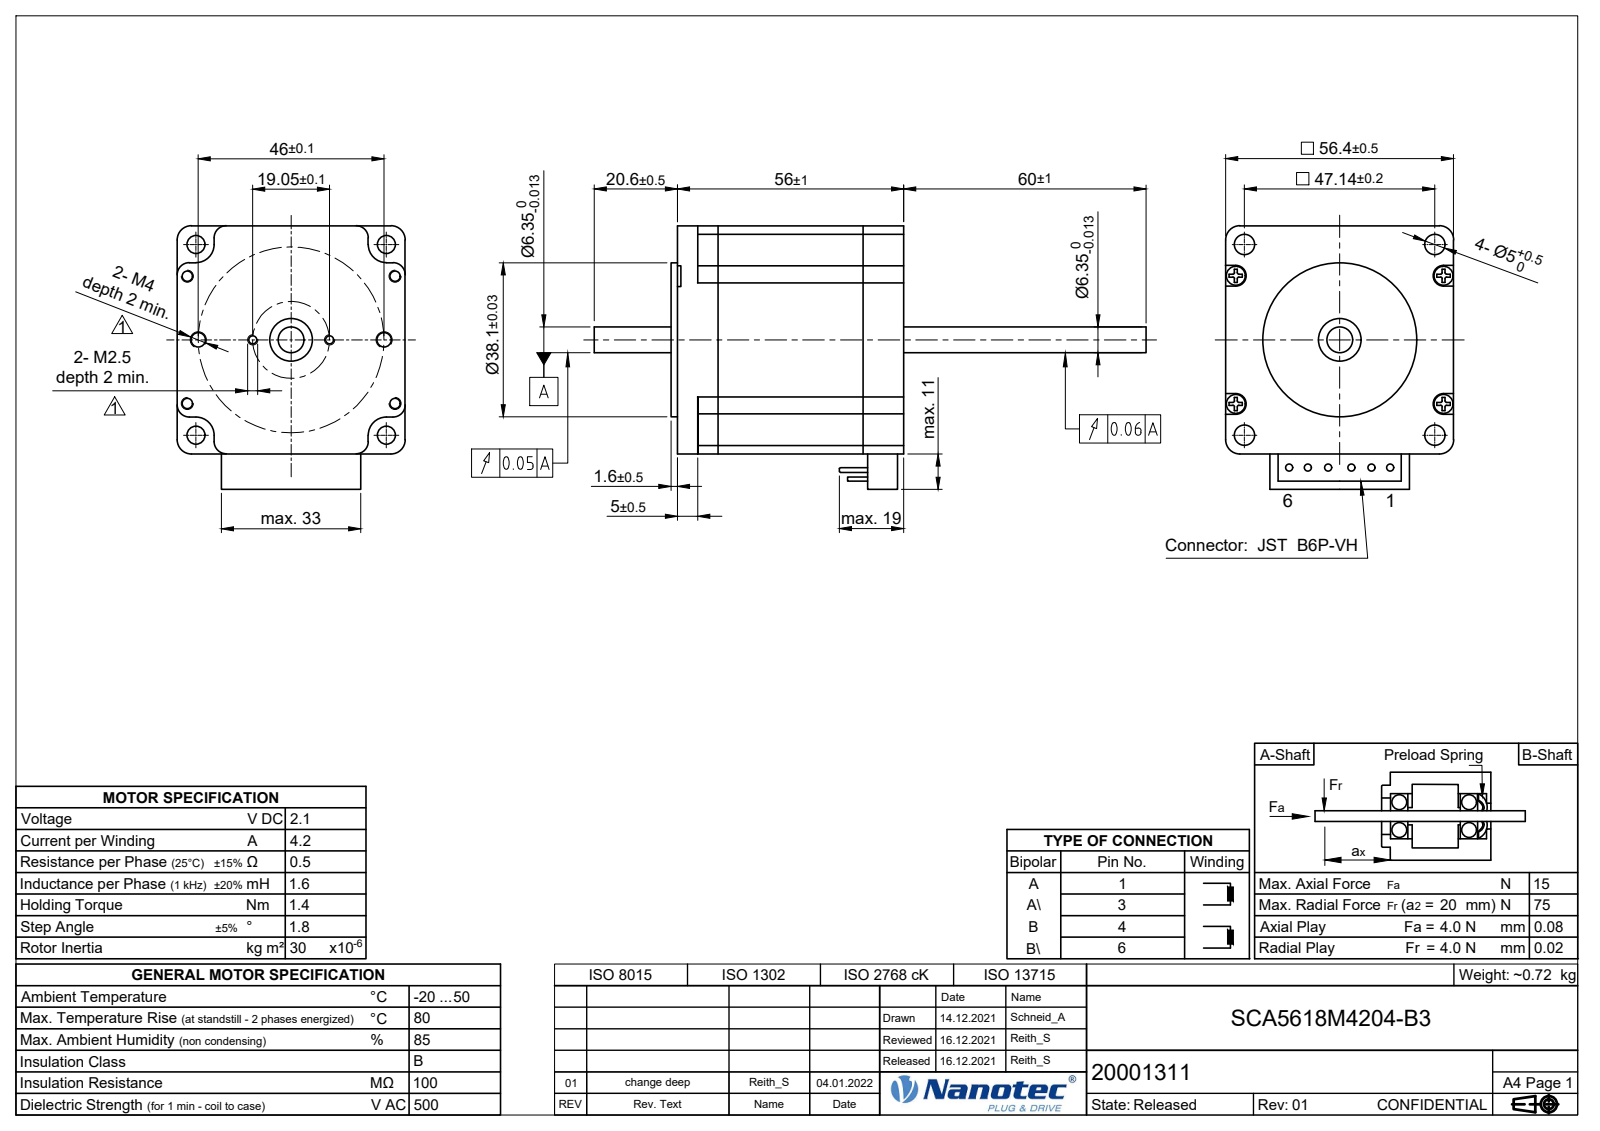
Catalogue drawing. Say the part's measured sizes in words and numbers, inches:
The part is named "SCA5618M-B3_Shrinkwrap_1". Its 3-D file was written by "Autodesk Inventor 2019 (AUTOMOTIVE_DESIGN)". It is 4 solids with 178 faces: 109 planar, 58 cylindrical and 11 other. Overall it measures 5.378 by 2.634 by 2.226 inches. Its volume is 10.31 cubic inches and its surface area 55.06 square inches. Round holes: 4 of diameter 0.098, 4 of diameter 0.126, 4 of diameter 0.197, 2 of diameter 0.079, 2 of diameter 0.128, 1 of diameter 0.079, 1 of diameter 0.323, 1 of diameter 0.413. Round bosses or shafts: 4 of diameter 0.22, 1 of diameter 1.5, 1 of diameter 0.25. Partial cylindrical surfaces (rounded edges, fillets, slot ends): 12 of radius 0.091, 8 of radius 0.079, 4 of radius 0.126, 4 of radius 0.197. The main face-to-face distances are 1.555, 2.22, 2.008, 0.453, 0.197, 1.752, 2.205, 0.063, 0.26, 1.815. The hole center spacings are 0.313, 0.632, 0.885, 0.928, 1.08, 1.181, 1.312, 1.513.
